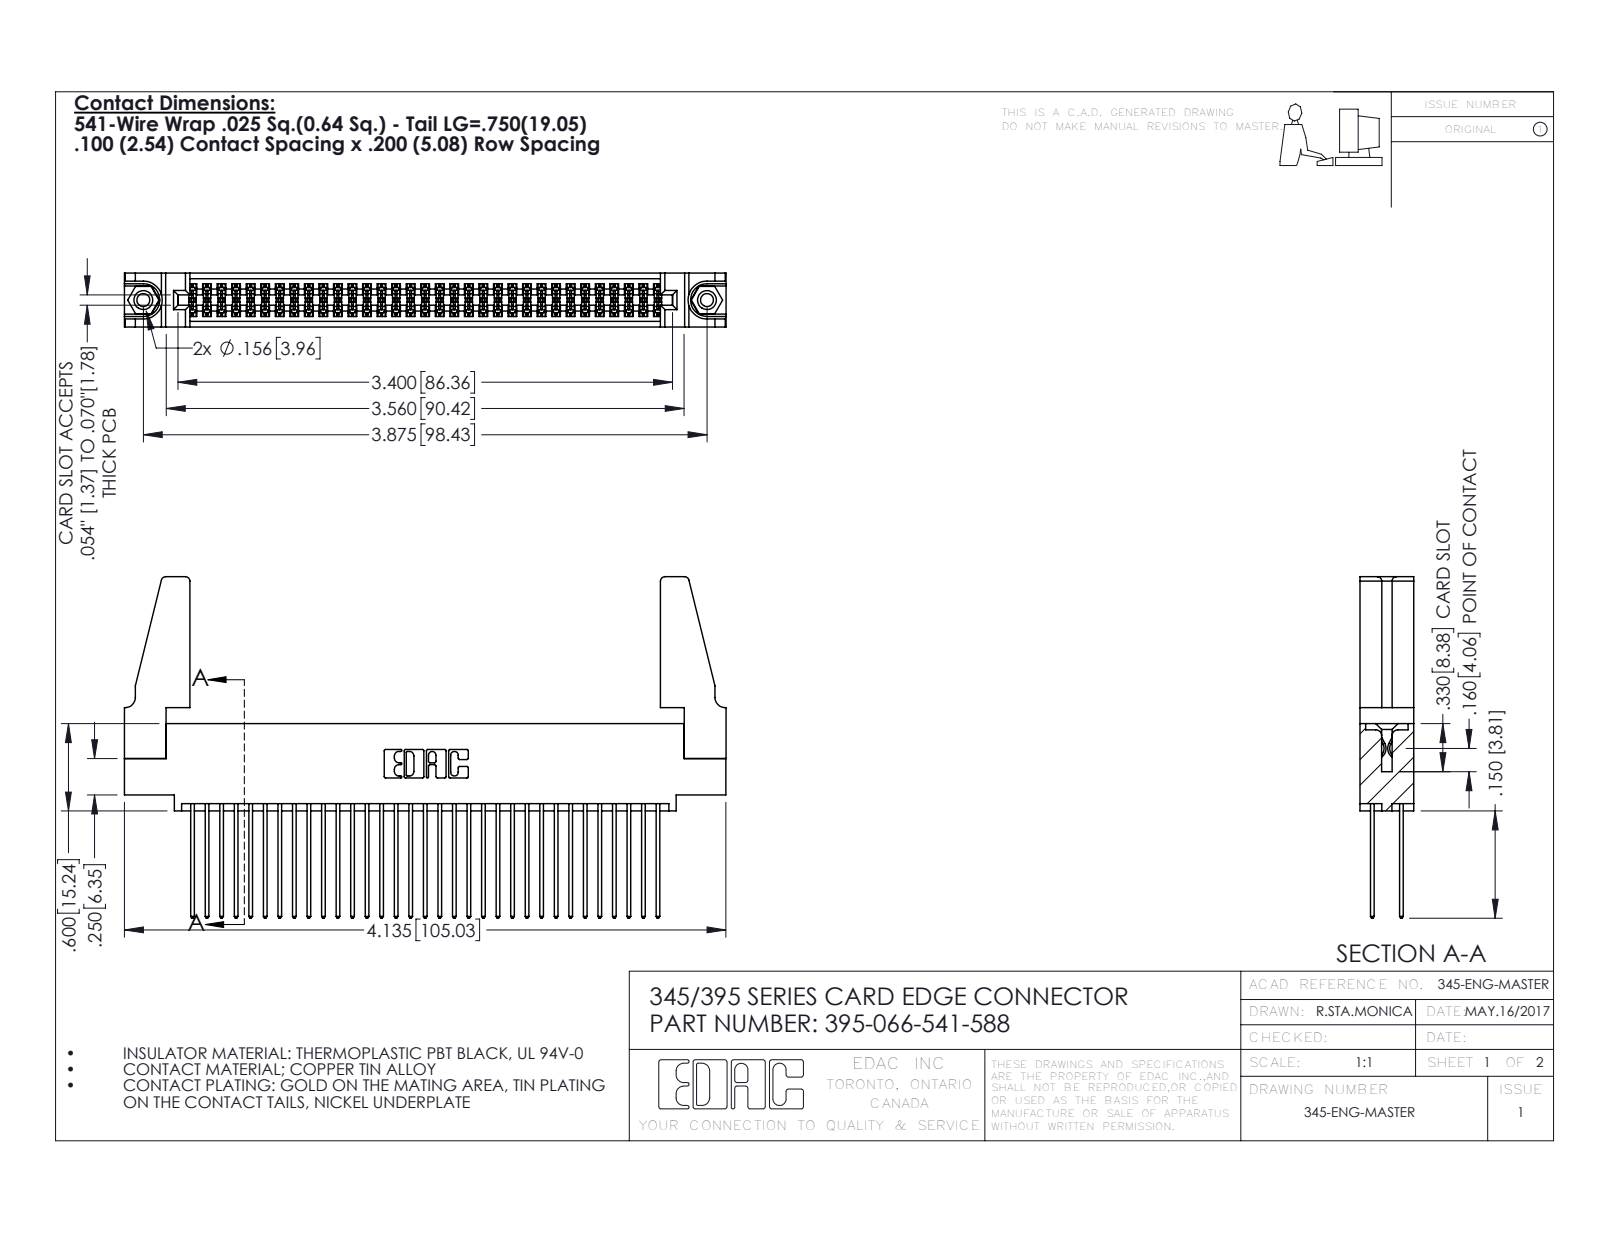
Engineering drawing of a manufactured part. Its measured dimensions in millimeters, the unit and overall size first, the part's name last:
Units: millimetres
Overall size (bounding box): 105.1 × 59.6 × 9.4
Round holes (diameter × count): ⌀2.3 ×2, ⌀3.2 ×2, ⌀4 ×2, ⌀1.6 ×1
Round bosses / shafts (diameter × count): ⌀3.9 ×2
Partial cylindrical surfaces — rounded edges, fillets, slot ends (radius × count): R0.2 ×99, R0.3 ×66, R0.3 ×22, R0.8 ×8, R0.2 ×6, R0.8 ×6, R0.7 ×3, R0.4 ×2
Main face-to-face distances: 1.8, 7.6, 5.1, 2.5, 6.9, 0.6, 9.4, 5.7, 4.4, 3.8
Hole centre spacings: 6.9, 92.5, 98.4
Volume: 13 700 mm³ · Surface area: 20 230 mm²
Bodies: 71 solids, 3554 faces (2334 planar, 1204 cylindrical, 16 other)
Part name (STEP PRODUCT): 345-250-001_345-250-001-102; 345-220-078_345-220-088; 345-292-001_345-293-141; 395-066-541-588 (+1 more)
STEP written by: SolidWorks 2016 (CONFIG_CONTROL_DESIGN)
